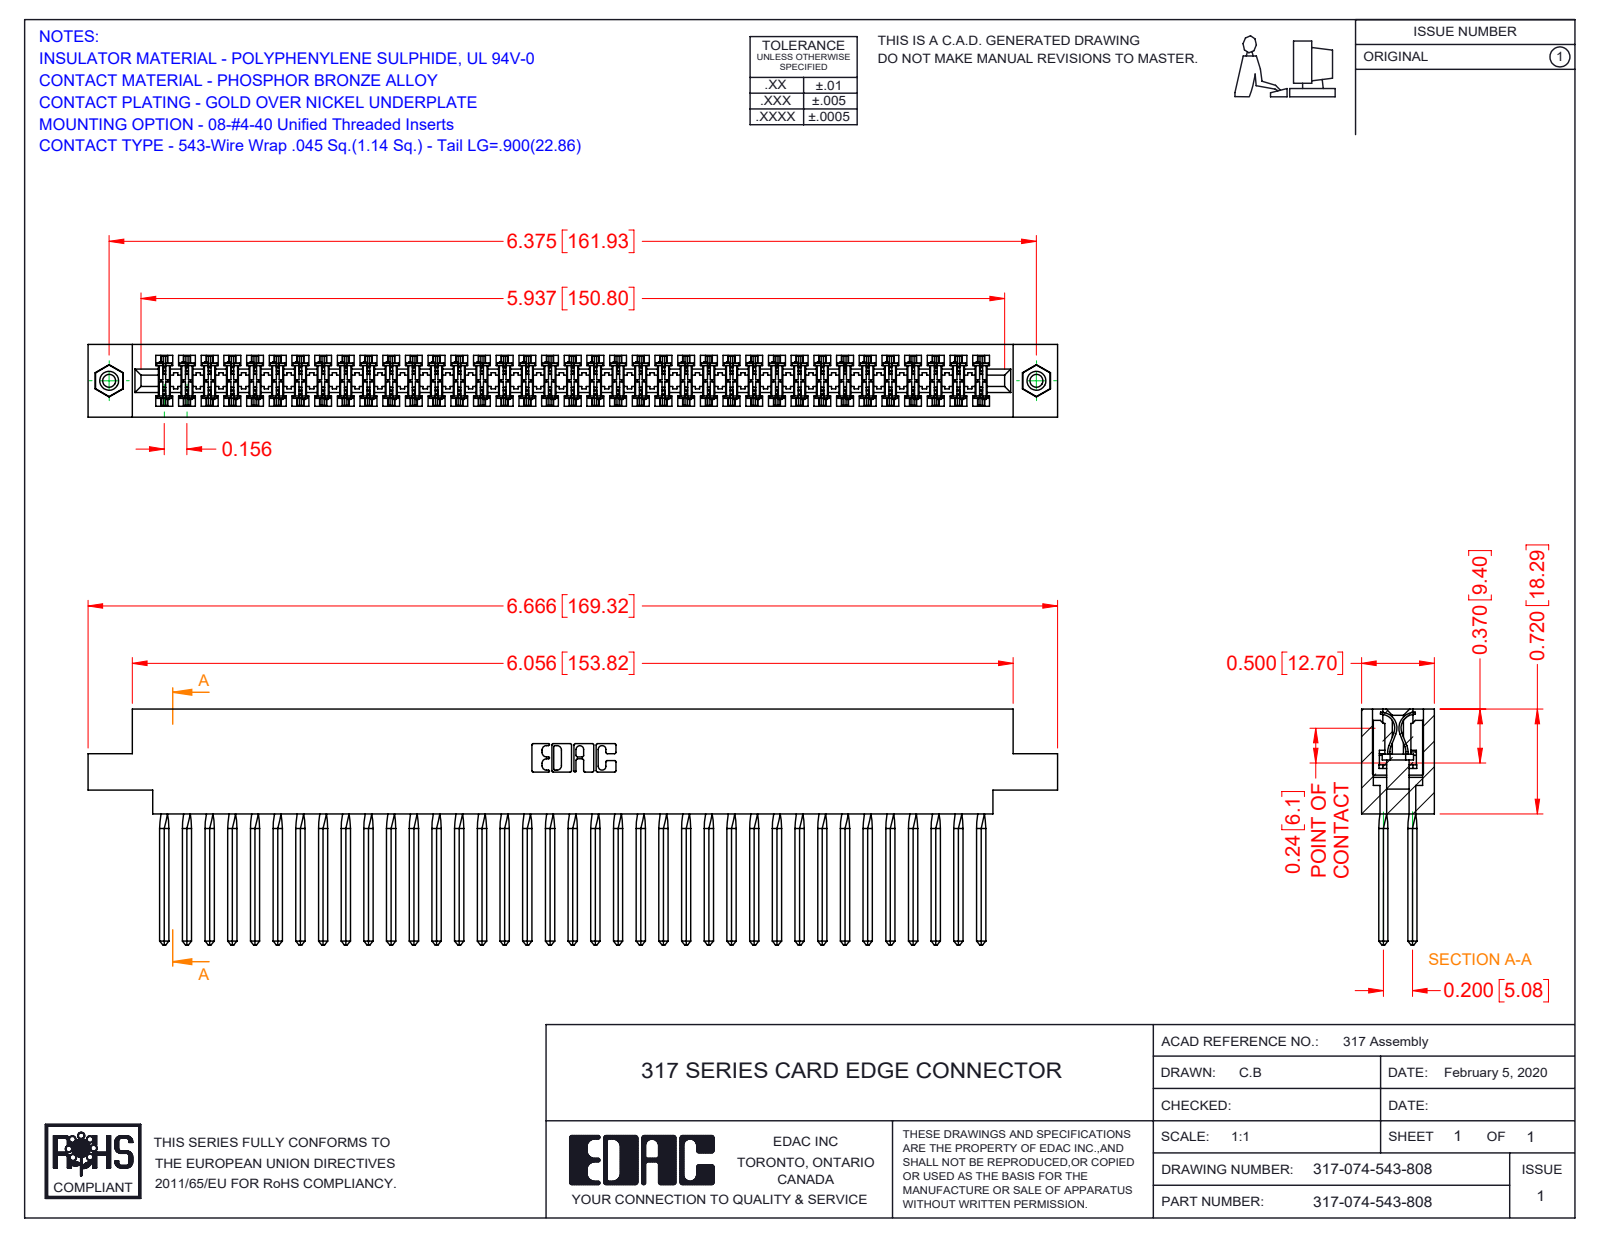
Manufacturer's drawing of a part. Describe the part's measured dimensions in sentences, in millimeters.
The part is named "317-290-001_543; 317 Part_.156 Dia - TI; 317-074-543-808; 345-250-001_345-250-003-102". Its 3-D file was written by "SolidWorks 2016 (CONFIG_CONTROL_DESIGN)". It is 77 solids with 6748 faces: 5492 planar, 944 cylindrical and 312 other. Overall it measures 169.3 by 41.1 by 12.7 millimeters. Its volume is 28 610 cubic millimeters and its surface area 43 230 square millimeters. Round holes: 2 of diameter 2.3, 2 of diameter 3.2, 2 of diameter 4. Round bosses or shafts: 2 of diameter 3.9. Partial cylindrical surfaces (rounded edges, fillets, slot ends): 148 of radius 0.4, 22 of radius 0.3, 6 of radius 0.2, 6 of radius 0.8, 3 of radius 0.7, 2 of radius 2.4, 2 of radius 2.5, 2 of radius 2.8. The main face-to-face distances are 12.7, 1.9, 10.8, 8.9, 2.8, 5, 2.4, 5.1, 2.9, 3.3. The hole center spacings are 161.9.
